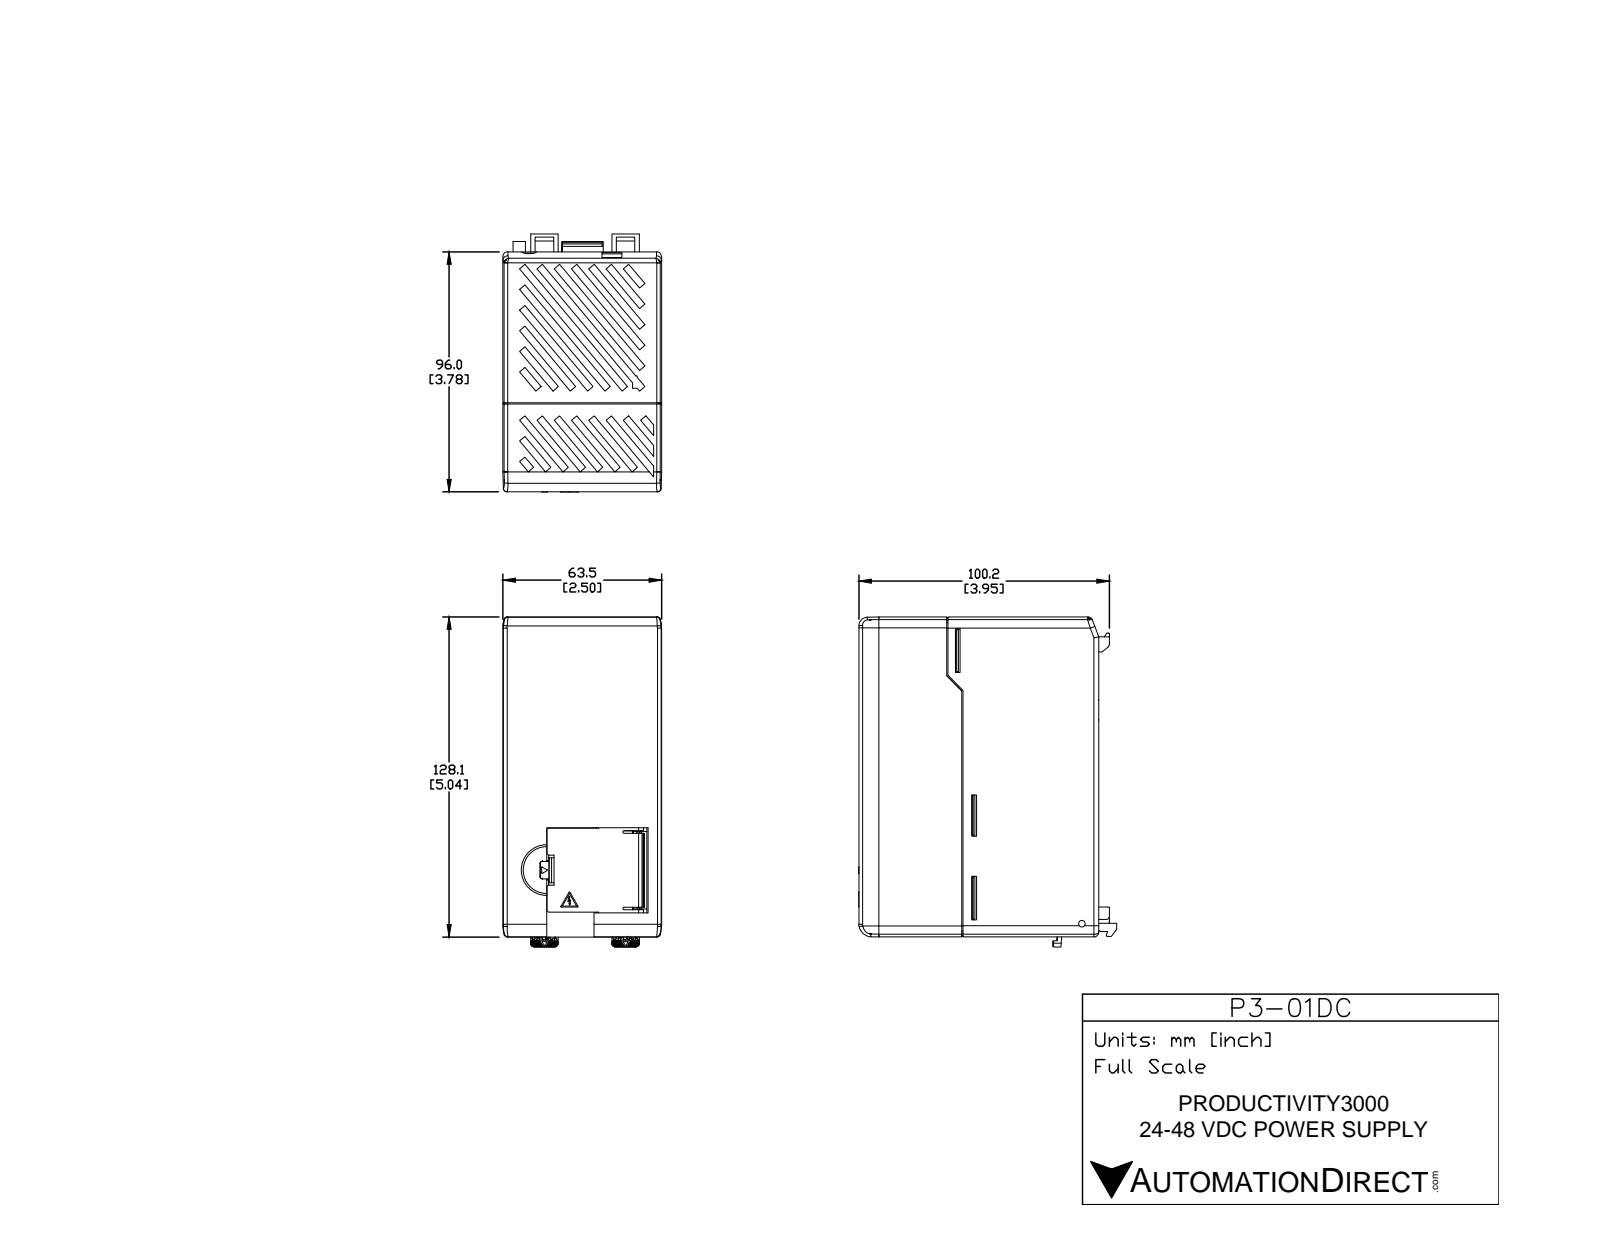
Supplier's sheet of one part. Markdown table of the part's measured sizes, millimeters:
| quantity | value |
| --- | --- |
| part name | P3-01DC |
| STEP written by | SolidWorks 2009 (CONFIG_CONTROL_DESIGN) |
| units | millimeters |
| bodies | 1 solid, 1485 faces (1280 planar, 164 cylindrical, 41 other) |
| overall size | 132.08 × 103.27 × 63.5 |
| volume | 760 237 mm³ |
| surface area | 64 605 mm² |
| round holes (diameter × count) | 2 × 4, 2.6 × 1 |
| round bosses / shafts (diameter × count) | 5.6 × 4 |
| partial cylindrical surfaces (radius × count) | 0.5 × 26, 1 × 22, 1.5 × 10, 0.2 × 6, 1.2 × 6, 2 × 6, 11.7 × 4, 12 × 4 |
| main face-to-face distances | 0.5, 63.5, 96.03, 63, 127.58, 128.08, 127.08, 95.93, 82.64, 13.29 |
| hole center spacings | 7.62, 15.24, 22.86 |
